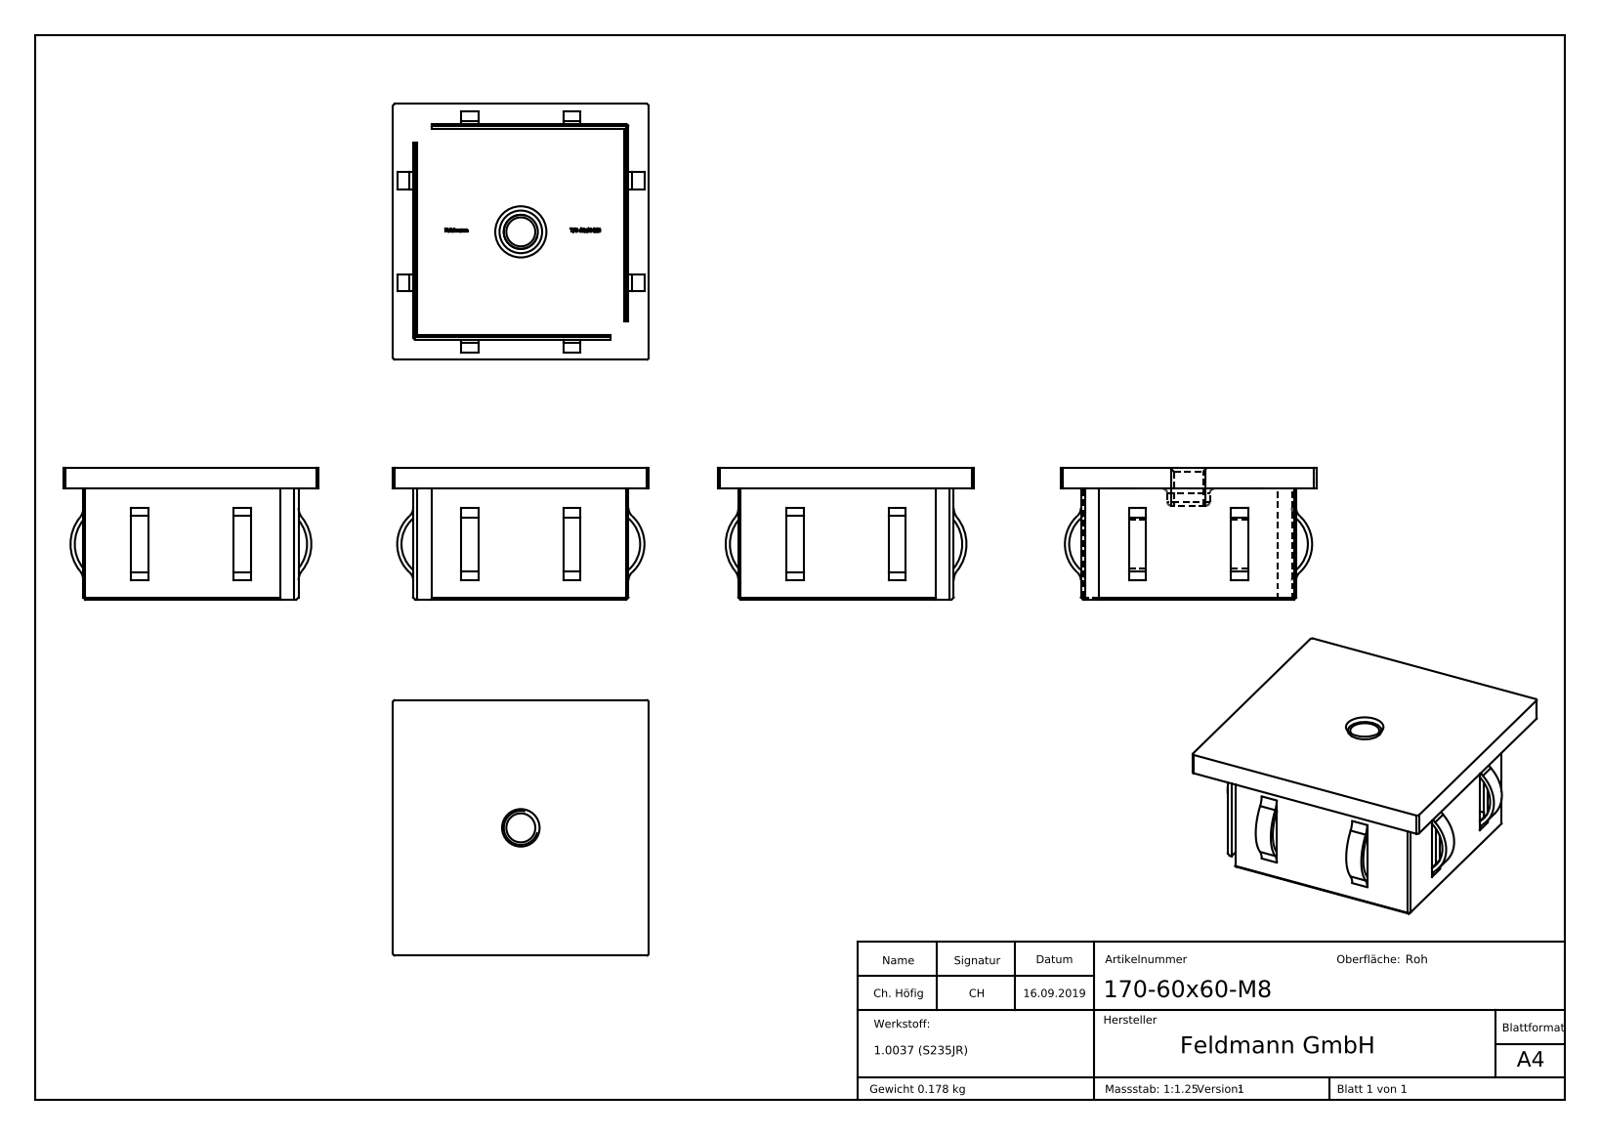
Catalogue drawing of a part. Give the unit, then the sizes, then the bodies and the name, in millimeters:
Units: millimetres
Overall size (bounding box): 60 × 60 × 31
Round holes (diameter × count): ⌀6.8 ×1
Round bosses / shafts (diameter × count): ⌀10 ×1
Partial cylindrical surfaces — rounded edges, fillets, slot ends (radius × count): R0.5 ×6, R2.51 ×4, R3.51 ×4, R3.54 ×4, R4.54 ×4, R9 ×4, R8 ×2, R10 ×2
Main face-to-face distances: 1, 49.5, 5, 48.5, 50.5, 4.75, 5.75, 54.25, 55.25, 60
Volume: 22 763 mm³ · Surface area: 18 731 mm²
Bodies: 1 solid, 376 faces (192 planar, 66 cylindrical, 118 other)
Part name (STEP PRODUCT): 170-60x60-M8
STEP written by: SolidWorks 2015 (CONFIG_CONTROL_DESIGN)
